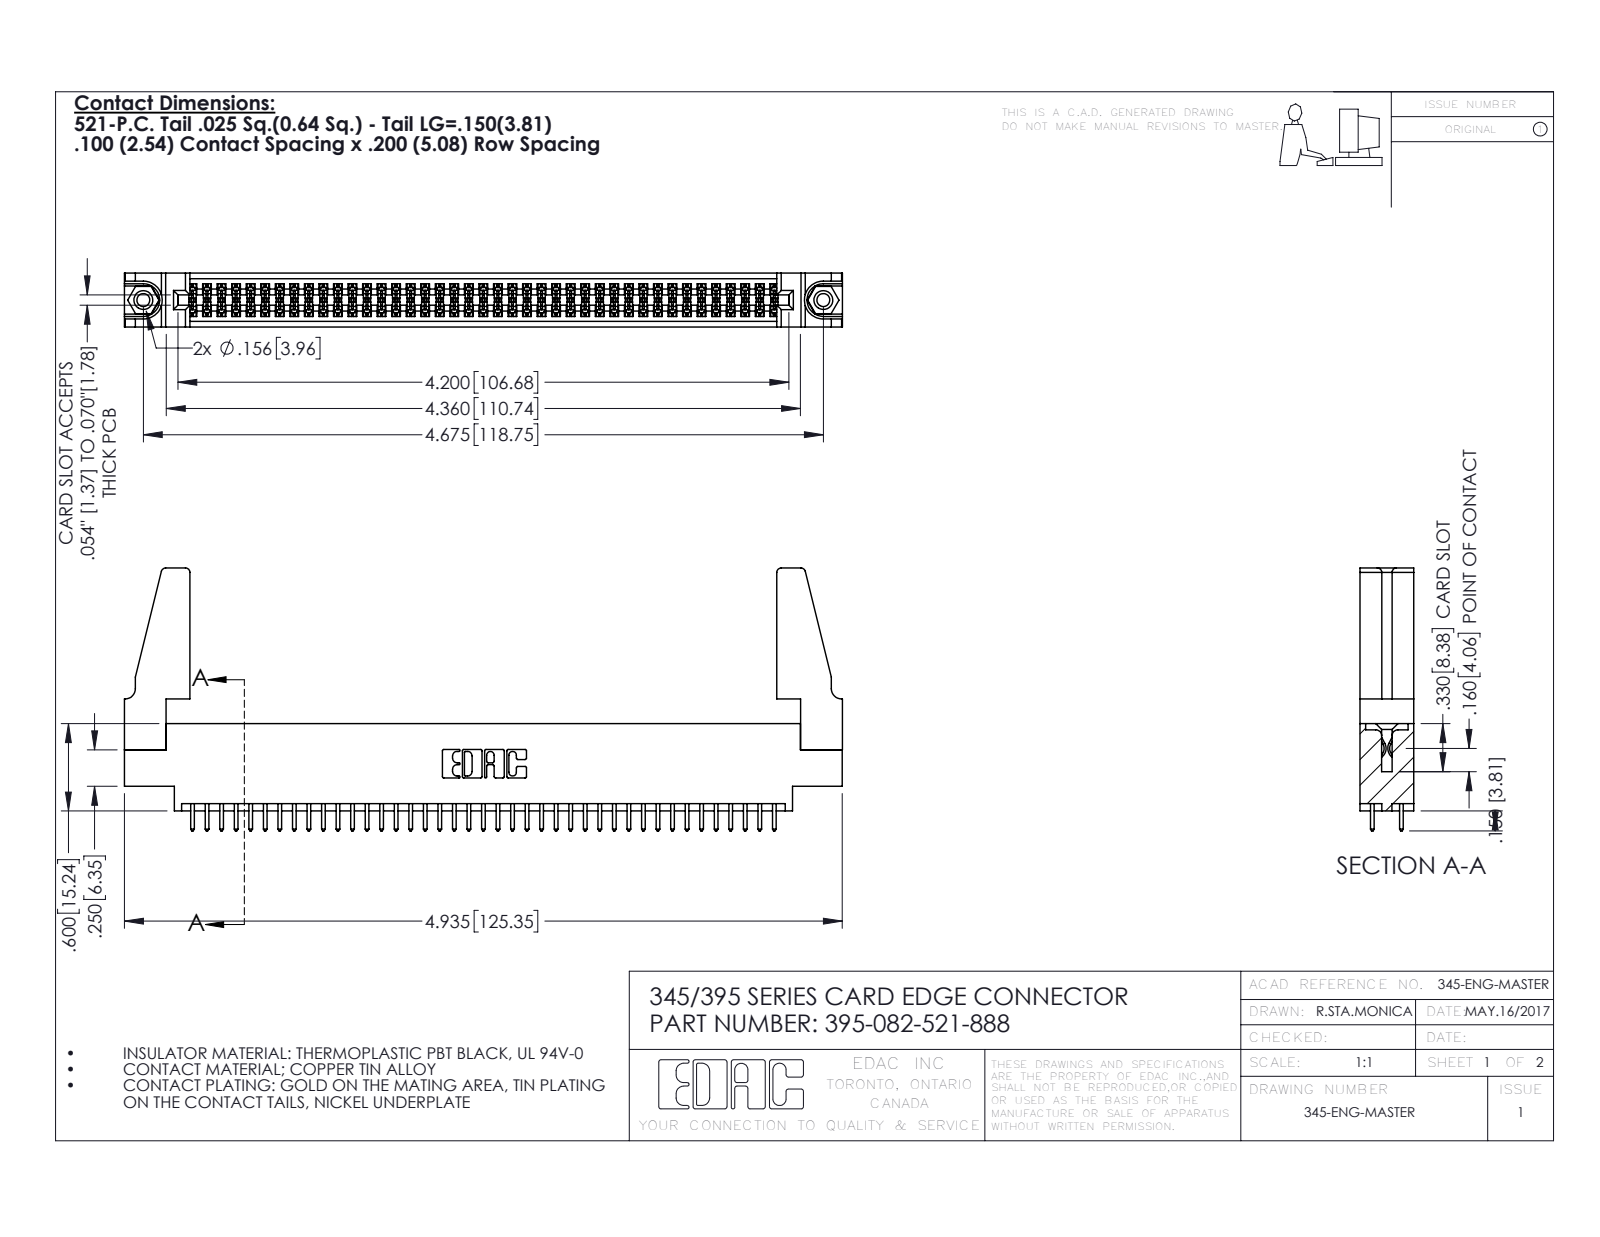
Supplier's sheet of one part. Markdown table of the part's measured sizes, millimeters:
| quantity | value |
| --- | --- |
| part name | 345 Part_0.170 Offset - 0.156 Dia-TH; 395-082-521-888; 345-250-001_345-250-001-102; 345-292-001_345-293-121 (+1 more) |
| STEP written by | SolidWorks 2016 (CONFIG_CONTROL_DESIGN) |
| units | millimeters |
| bodies | 87 solids, 4354 faces (2862 planar, 1476 cylindrical, 16 other) |
| overall size | 125.4 × 45.9 × 9.4 |
| volume | 15 300 mm³ |
| surface area | 20 800 mm² |
| round holes (diameter × count) | 2.3 × 2, 3.2 × 2, 4 × 2, 1.6 × 1 |
| round bosses / shafts (diameter × count) | 3.9 × 2 |
| partial cylindrical surfaces (radius × count) | 0.2 × 123, 0.3 × 82, 0.3 × 22, 0.8 × 8, 0.2 × 6, 0.8 × 6, 0.7 × 3, 0.4 × 2 |
| main face-to-face distances | 1.8, 7.6, 9.4, 5.1, 2.5, 6.9, 0.6, 5.7, 4.4, 3.8 |
| hole center spacings | 6.9, 112.8, 118.7 |
